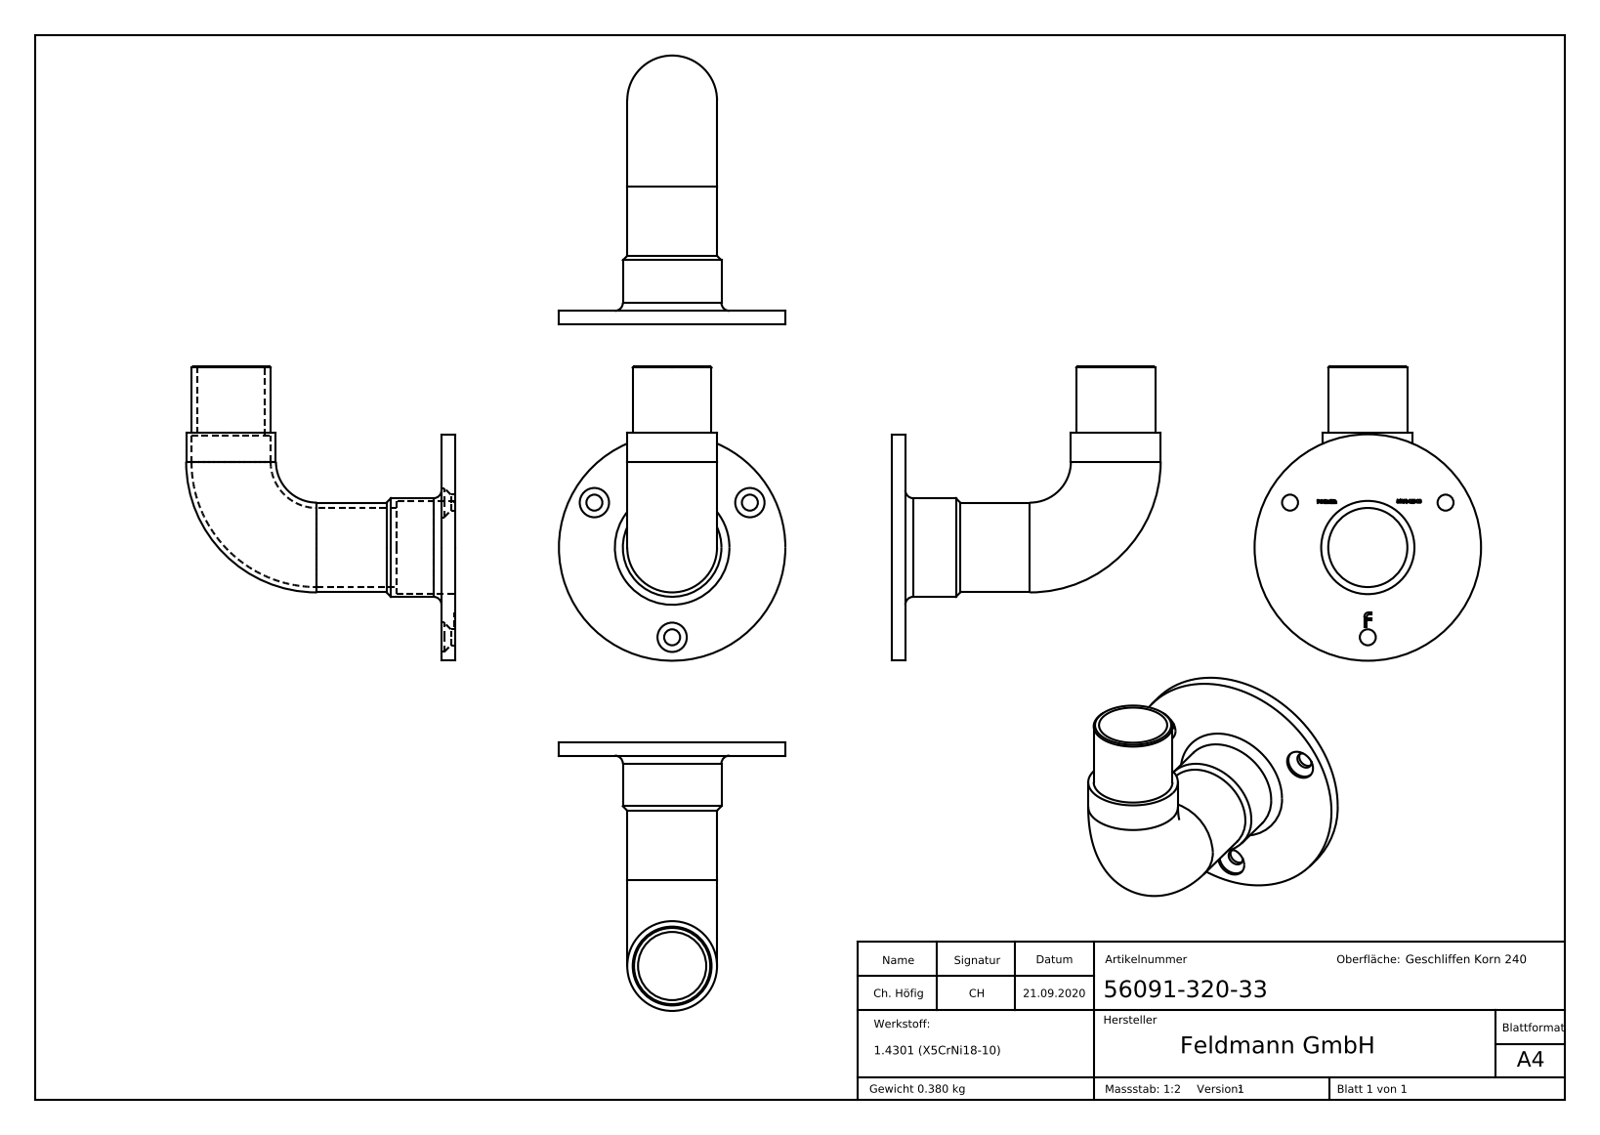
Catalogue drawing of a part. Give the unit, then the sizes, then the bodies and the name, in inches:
Units: inches
Overall size (bounding box): 4.35 × 3.97 × 3.346
Round holes (diameter × count): ⌀0.236 ×3, ⌀0.433 ×3, ⌀1.169 ×2, ⌀1.008 ×1, ⌀1.378 ×1
Round bosses / shafts (diameter × count): ⌀1.327 ×2, ⌀3.346 ×1, ⌀1.457 ×1, ⌀1.165 ×1
Main face-to-face distances: 0.197, 0.866, 0.669, 0.039, 1.024, 0.984, 0.193, 0.862, 0.036, 0.03
Hole centre spacings: 1.327, 2.298, 2.298
Volume: 2.932 in³ · Surface area: 59.51 in²
Bodies: 1 solid, 304 faces (139 planar, 15 cylindrical, 150 other)
Part name (STEP PRODUCT): 56091-320-33
STEP written by: SolidWorks 2018 (CONFIG_CONTROL_DESIGN)
